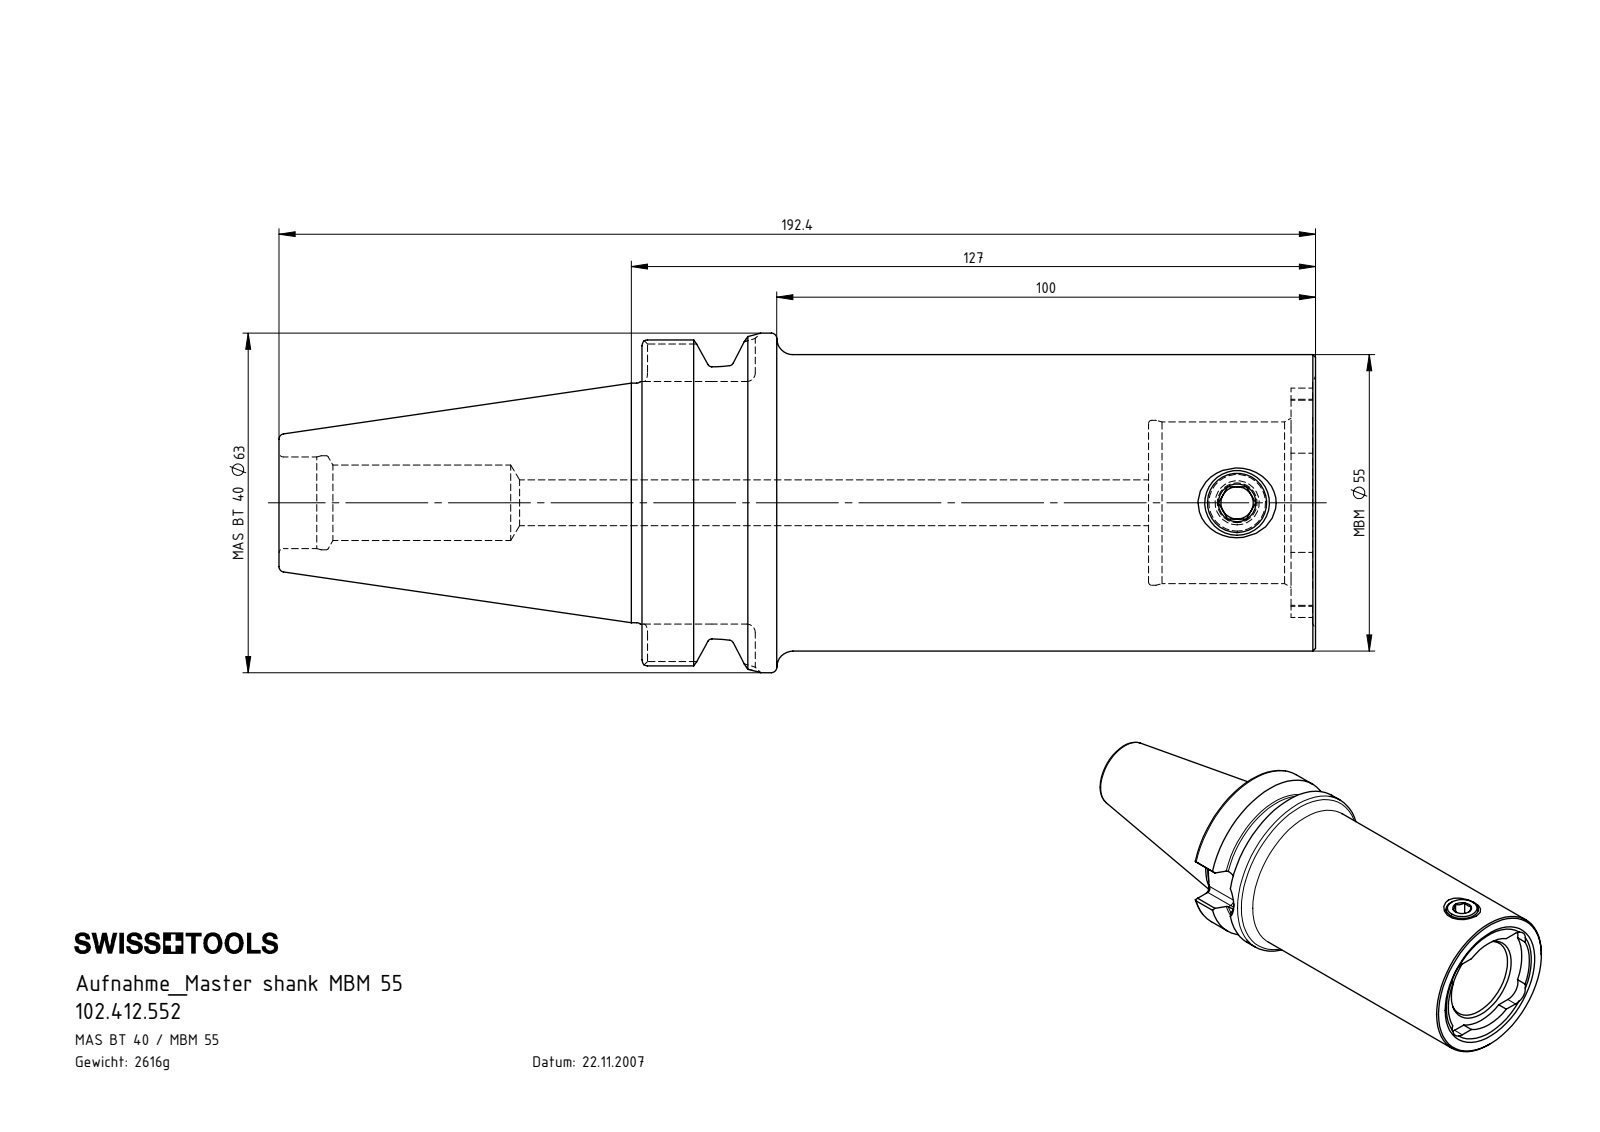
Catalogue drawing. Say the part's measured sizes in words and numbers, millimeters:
The part is named "BB4-MB5.K01.127_C; 102.412.552; MB5-ER1.001.017_A; ISO 4026 - M5 x 5_PreviewCfg (+1 more)". Its 3-D file was written by "SolidWorks 2017 (CONFIG_CONTROL_DESIGN)". It is 5 solids with 219 faces: 69 planar, 69 cylindrical and 81 other. Overall it measures 192.4 by 63 by 63 millimeters. Its volume is 332 578 cubic millimeters and its surface area 45 546 square millimeters. Round holes: 3 of diameter 4.2, 2 of diameter 3.3, 1 of diameter 6, 1 of diameter 8.5, 1 of diameter 11, 1 of diameter 14, 1 of diameter 17, 1 of diameter 17.45, 1 of diameter 30, 1 of diameter 30.6. Round bosses or shafts: 2 of diameter 4, 1 of diameter 63, 1 of diameter 55, 1 of diameter 53, 1 of diameter 44.45, 1 of diameter 12, 1 of diameter 5. Partial cylindrical surfaces (rounded edges, fillets, slot ends): 8 of radius 1.6, 4 of radius 5.2, 1 of radius 8.05, 1 of radius 18.5, 1 of radius 21.27. The main face-to-face distances are 94, 125, 31, 120.45, 26.45, 4.55, 124.45, 30.45, 4, 0.55.
